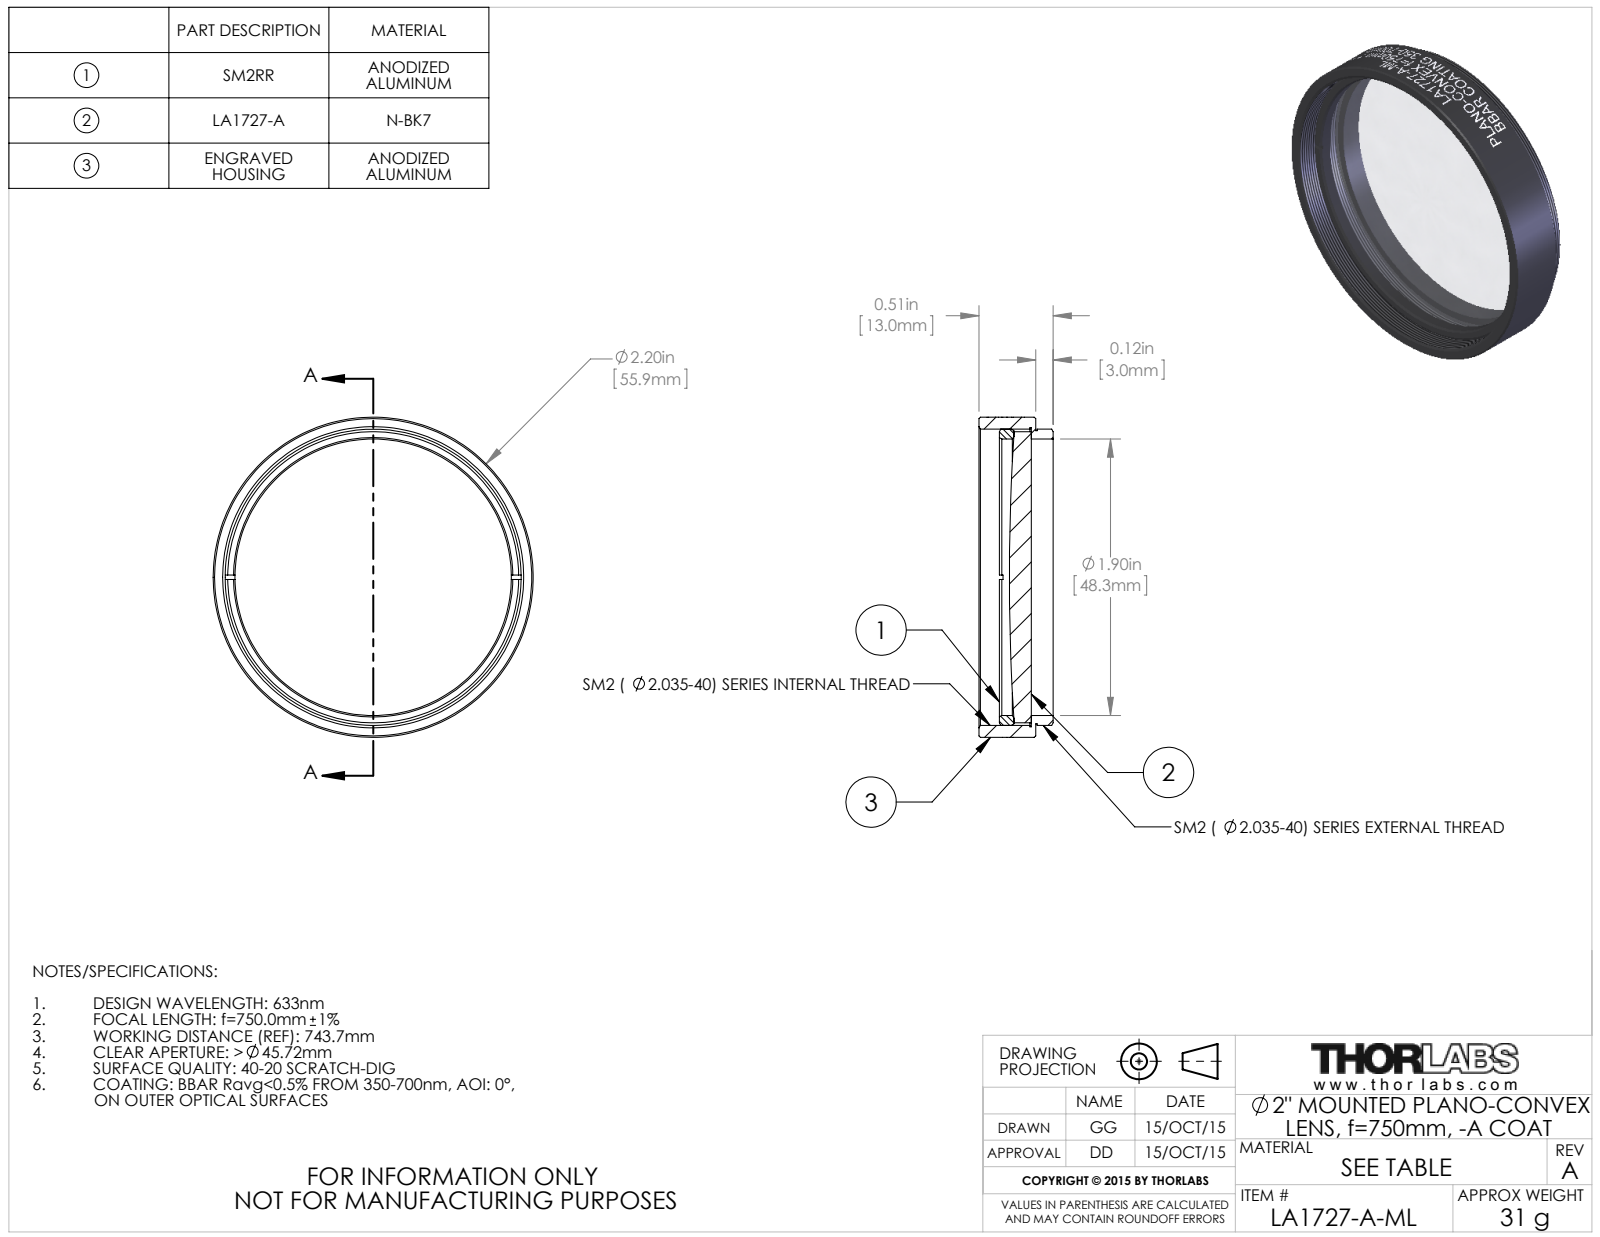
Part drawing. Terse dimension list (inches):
name: TTN039621-E0W
written by: SolidWorks 2014 (CONFIG_CONTROL_DESIGN)
unit: in
bodies: 3 solids, 140 faces (16 planar, 104 cylindrical, 20 other)
size: 2.2 × 2.2 × 0.51
volume: 0.735 in³; area: 17.59 in²
holes: 1× ⌀1.9, 1× ⌀2.055
bosses: 1× ⌀2.2, 1× ⌀2.035, 1× ⌀2.015, 1× ⌀2
face distances: 0.12, 0.15, 0.03, 0.39, 0.36, 0.51, 0.27, 0.24, 0.37, 0.25
